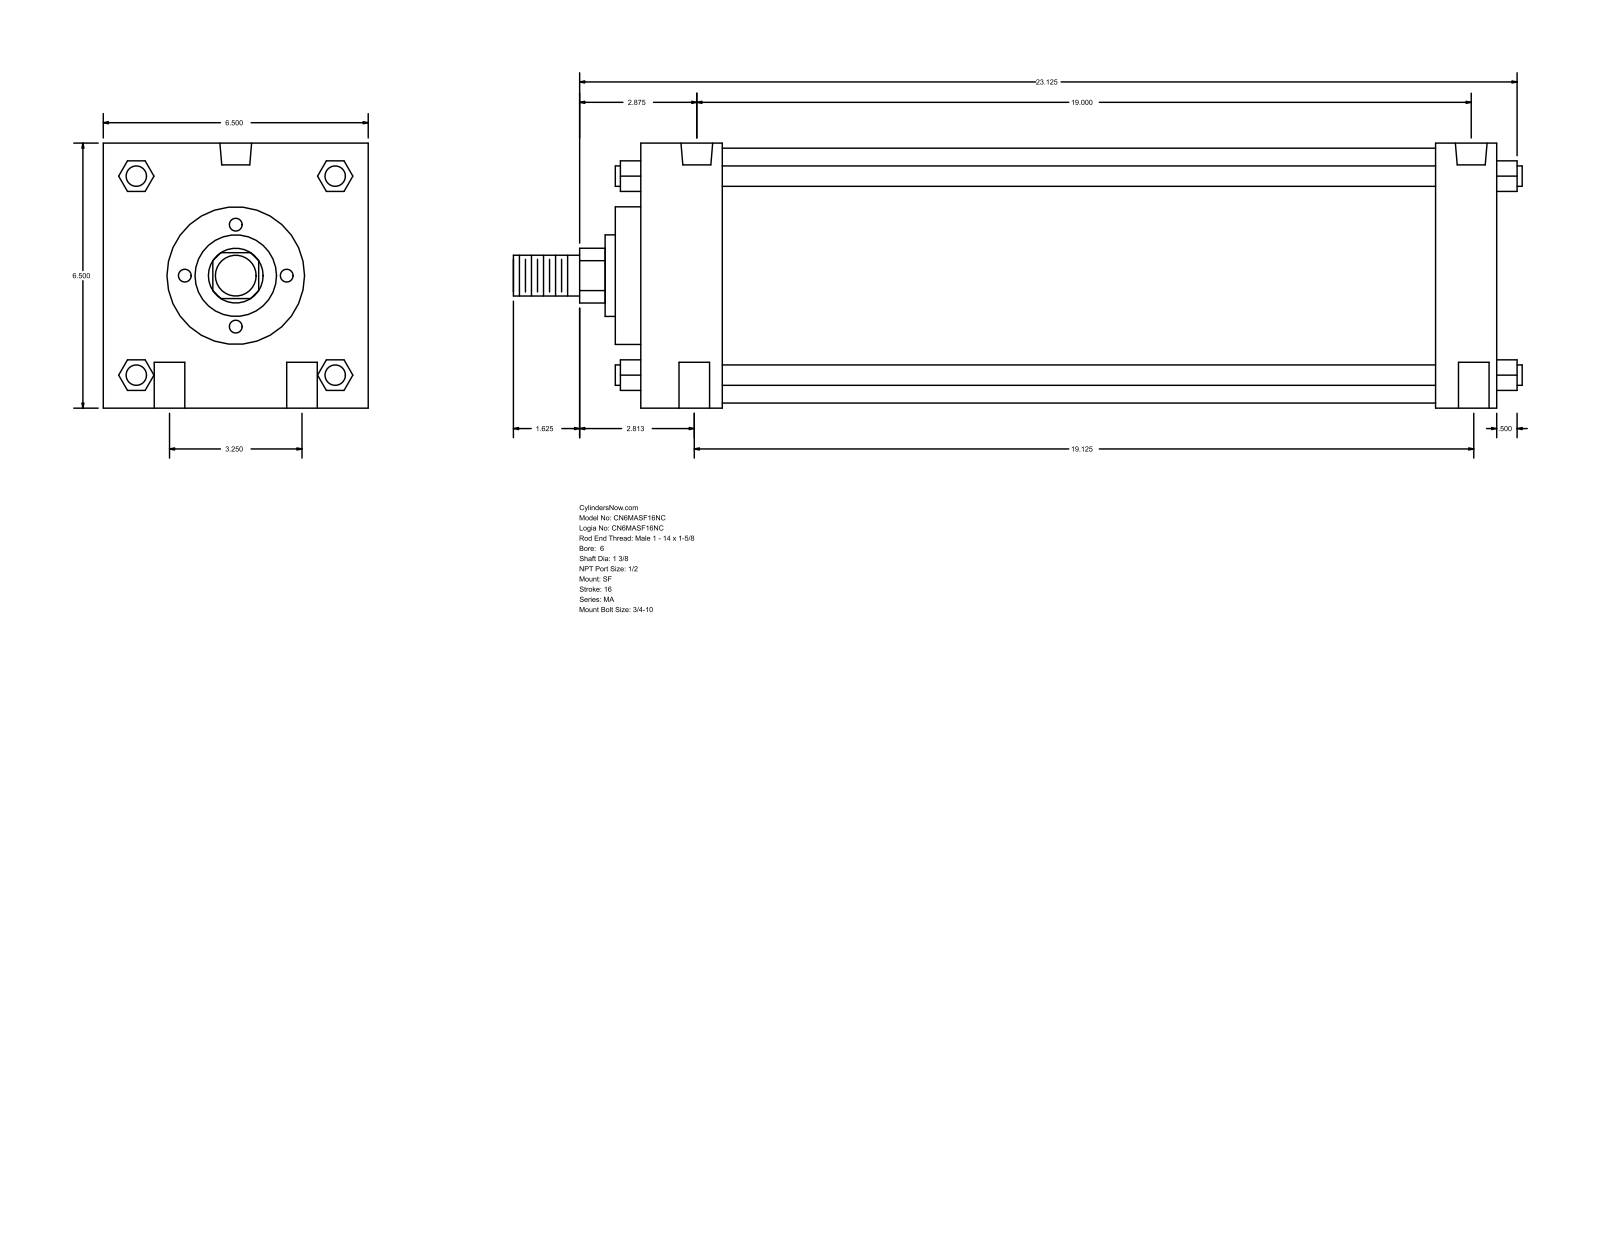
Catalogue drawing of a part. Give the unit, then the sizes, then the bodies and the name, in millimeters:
Units: millimetres
Overall size (bounding box): 628.65 × 165.1 × 165.1
Round holes (diameter × count): ⌀19.05 ×4, ⌀17.46 ×2, ⌀19.77 ×2
Round bosses / shafts (diameter × count): ⌀12.7 ×4, ⌀158.75 ×1, ⌀85.72 ×1, ⌀50.8 ×1, ⌀34.92 ×1, ⌀25.4 ×1
Partial cylindrical surfaces — rounded edges, fillets, slot ends (radius × count): R17.06 ×1
Main face-to-face distances: 165.1, 533.4, 495.3, 50.8, 38.1, 444.5, 482.6, 66.67, 15.87, 511.17
Hole centre spacings: 41.3, 485.94, 82.54, 485.77, 492.73, 482.59, 482.6
Bodies: 0 solids, 126 faces (95 planar, 31 cylindrical, 0 other)
Part name (STEP PRODUCT): MA_SF__0600_1.375
STEP written by: GSSL Pune (CONFIG_CONTROL_DESIGN)
